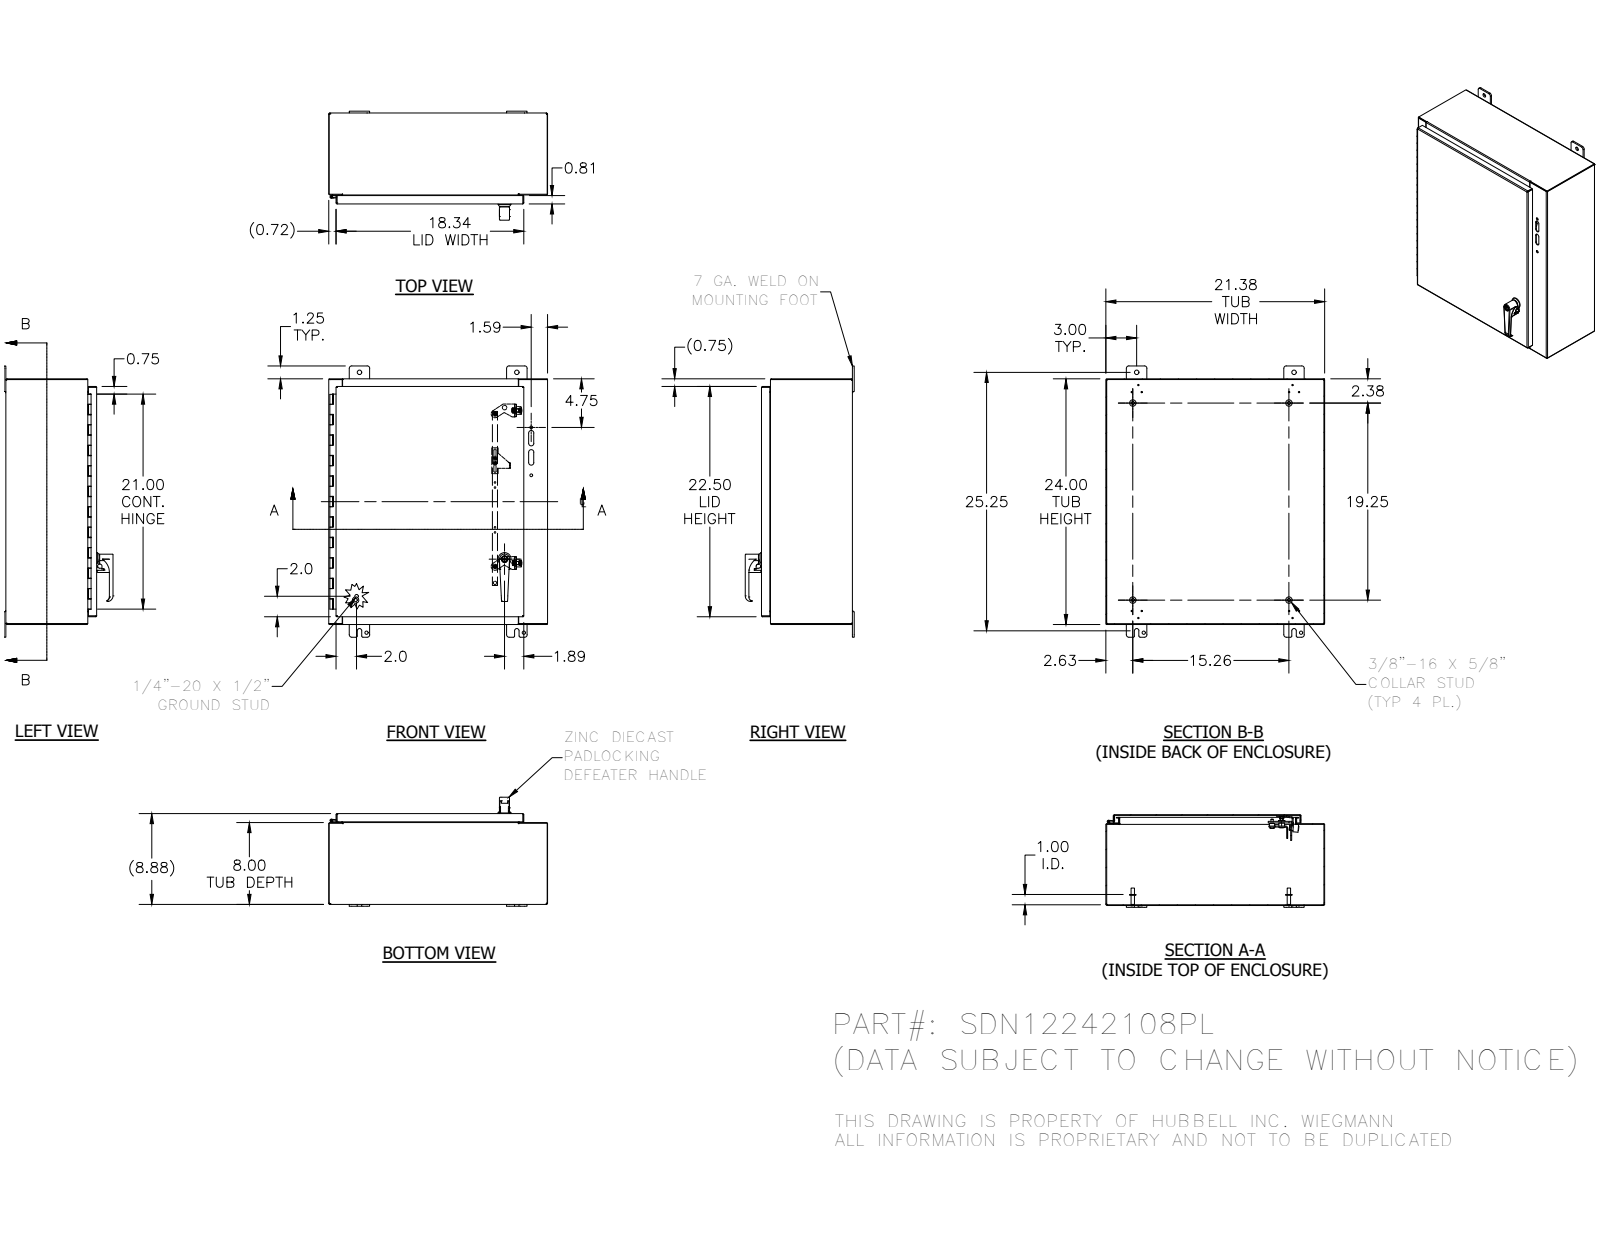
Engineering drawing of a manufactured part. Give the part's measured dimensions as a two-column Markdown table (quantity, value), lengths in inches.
| quantity | value |
| --- | --- |
| part name | SDN12242108PL |
| STEP written by | SolidWorks 2019 (AUTOMOTIVE_DESIGN) |
| units | inches |
| bodies | 49 solids, 1545 faces (792 planar, 525 cylindrical, 228 other) |
| overall size | 26.5 × 21.38 × 10.649 |
| volume | 153.5 in³ |
| surface area | 4 076 in² |
| round holes (diameter × count) | 0.12 × 12, 0.145 × 6, 0.313 × 4, 0.438 × 4, 0.32 × 3, 0.156 × 2, 0.196 × 2, 0.211 × 2, 0.22 × 2, 0.281 × 2, 0.313 × 2, 0.45 × 2 |
| round bosses / shafts (diameter × count) | 0.33 × 5, 0.437 × 4, 0.3 × 4, 0.25 × 4, 0.19 × 4, 0.625 × 3, 0.225 × 3, 0.75 × 2 |
| partial cylindrical surfaces (radius × count) | 0.02 × 38, 0.012 × 31, 0.25 × 22, 0.031 × 20, 0.105 × 20, 0.125 × 17, 0.025 × 16, 0.07 × 8 |
| main face-to-face distances | 0.074, 8.801, 8.727, 8.875, 21.306, 23.926, 7.926, 0.875, 21.38, 21.232 |
| hole center spacings | 14.9, 0.759, 14.752, 15.38, 21.38, 21.402, 22.068, 22.075 |
